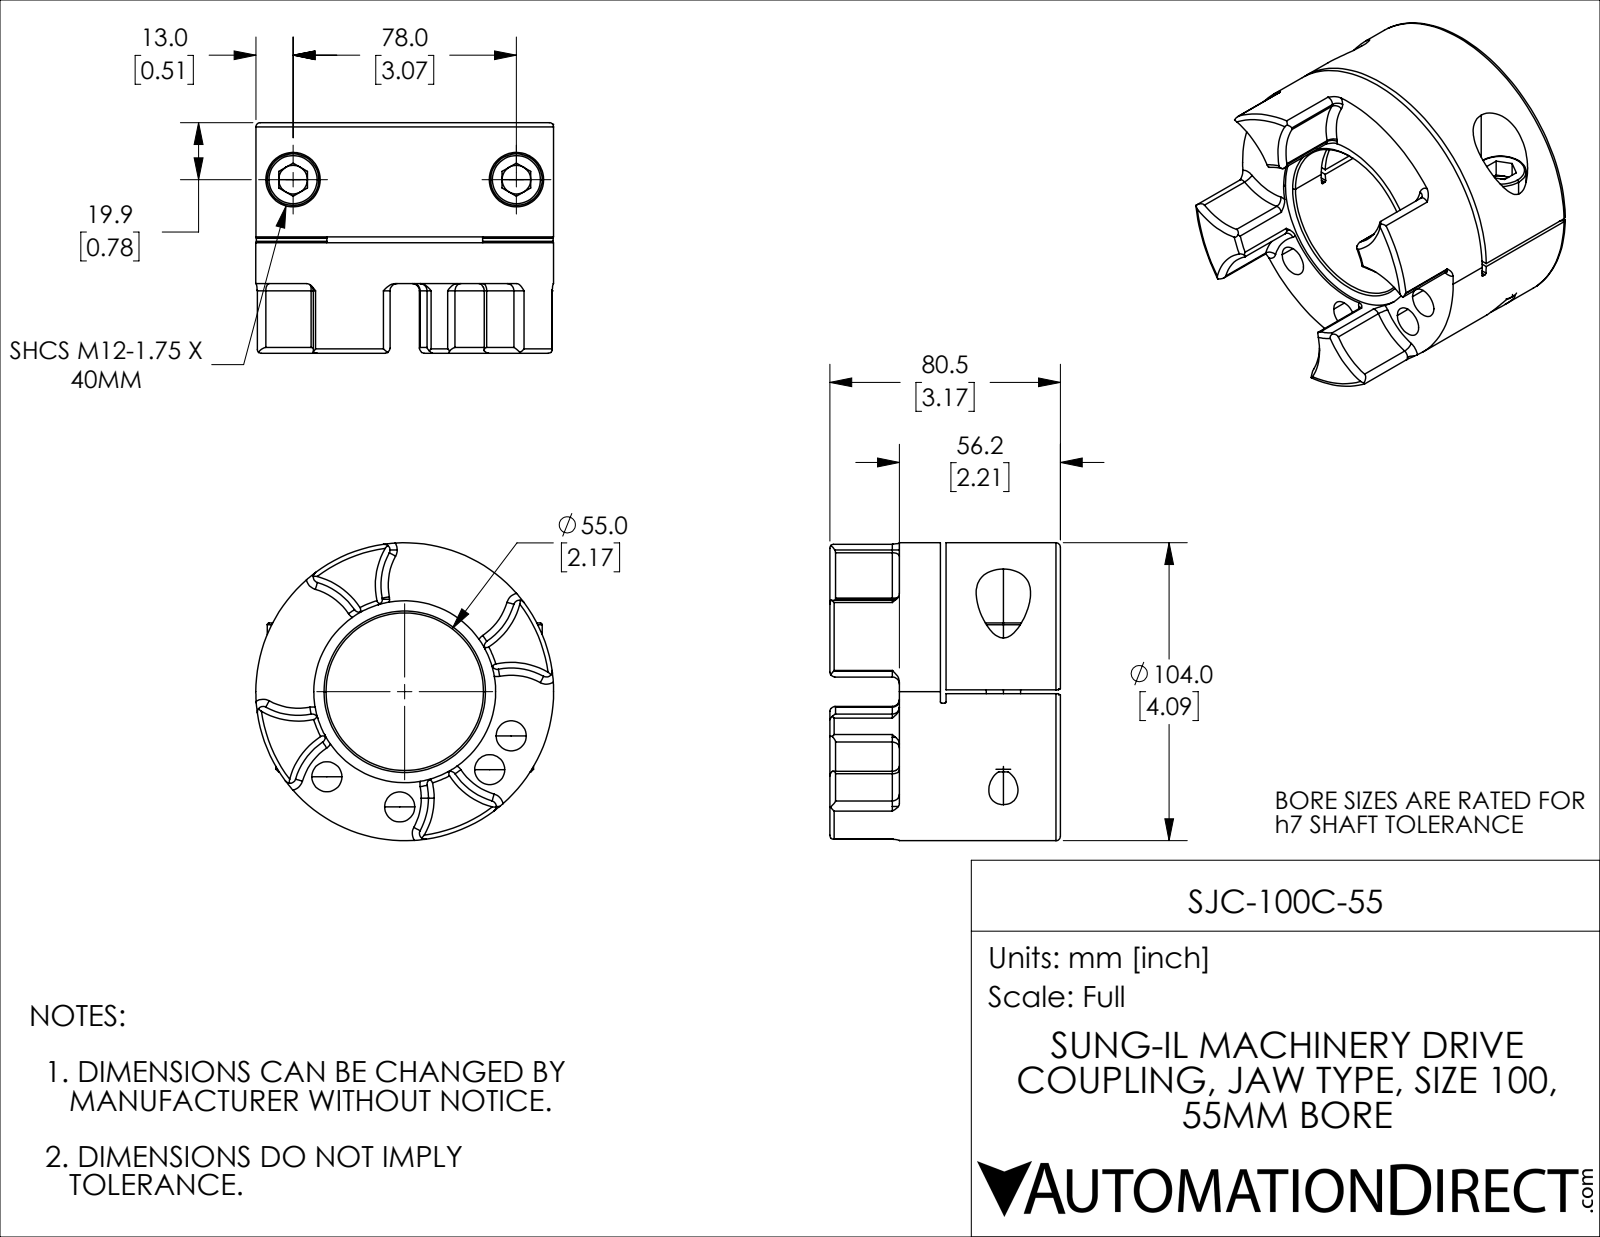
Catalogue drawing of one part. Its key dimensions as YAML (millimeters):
part_name: "SJC-100C-55"
step_written_by: "SolidWorks 2021 (CONFIG_CONTROL_DESIGN)"
units: millimeters
bodies: {solids: 4, faces: 222, planar: 55, cylindrical: 82, other: 85}
overall_size: [104, 104, 80.5]
volume: 354475
surface_area: 69641
round_holes:
  - {diameter: 10.5, count: 4}
  - {diameter: 10, count: 2}
  - {diameter: 10.2, count: 2}
  - {diameter: 12.5, count: 2}
  - {diameter: 19, count: 2}
  - {diameter: 55, count: 1}
  - {diameter: 63.5, count: 1}
round_bosses_or_shafts:
  - {diameter: 18, count: 2}
  - {diameter: 12, count: 2}
  - {diameter: 104, count: 1}
partial_cylinders:
  - {radius: 2, count: 16}
  - {radius: 23.68, count: 4}
  - {radius: 0.5, count: 2}
  - {radius: 75, count: 1}
face_to_face_distances: [2, 41.9, 39.9, 56.2, 16.3, 14.3, 0.35, 1.65, 80.5, 40.6]
hole_center_spacings: [40.25, 13.98, 27.52, 34.03, 46.18, 56.92, 65.94, 78]
